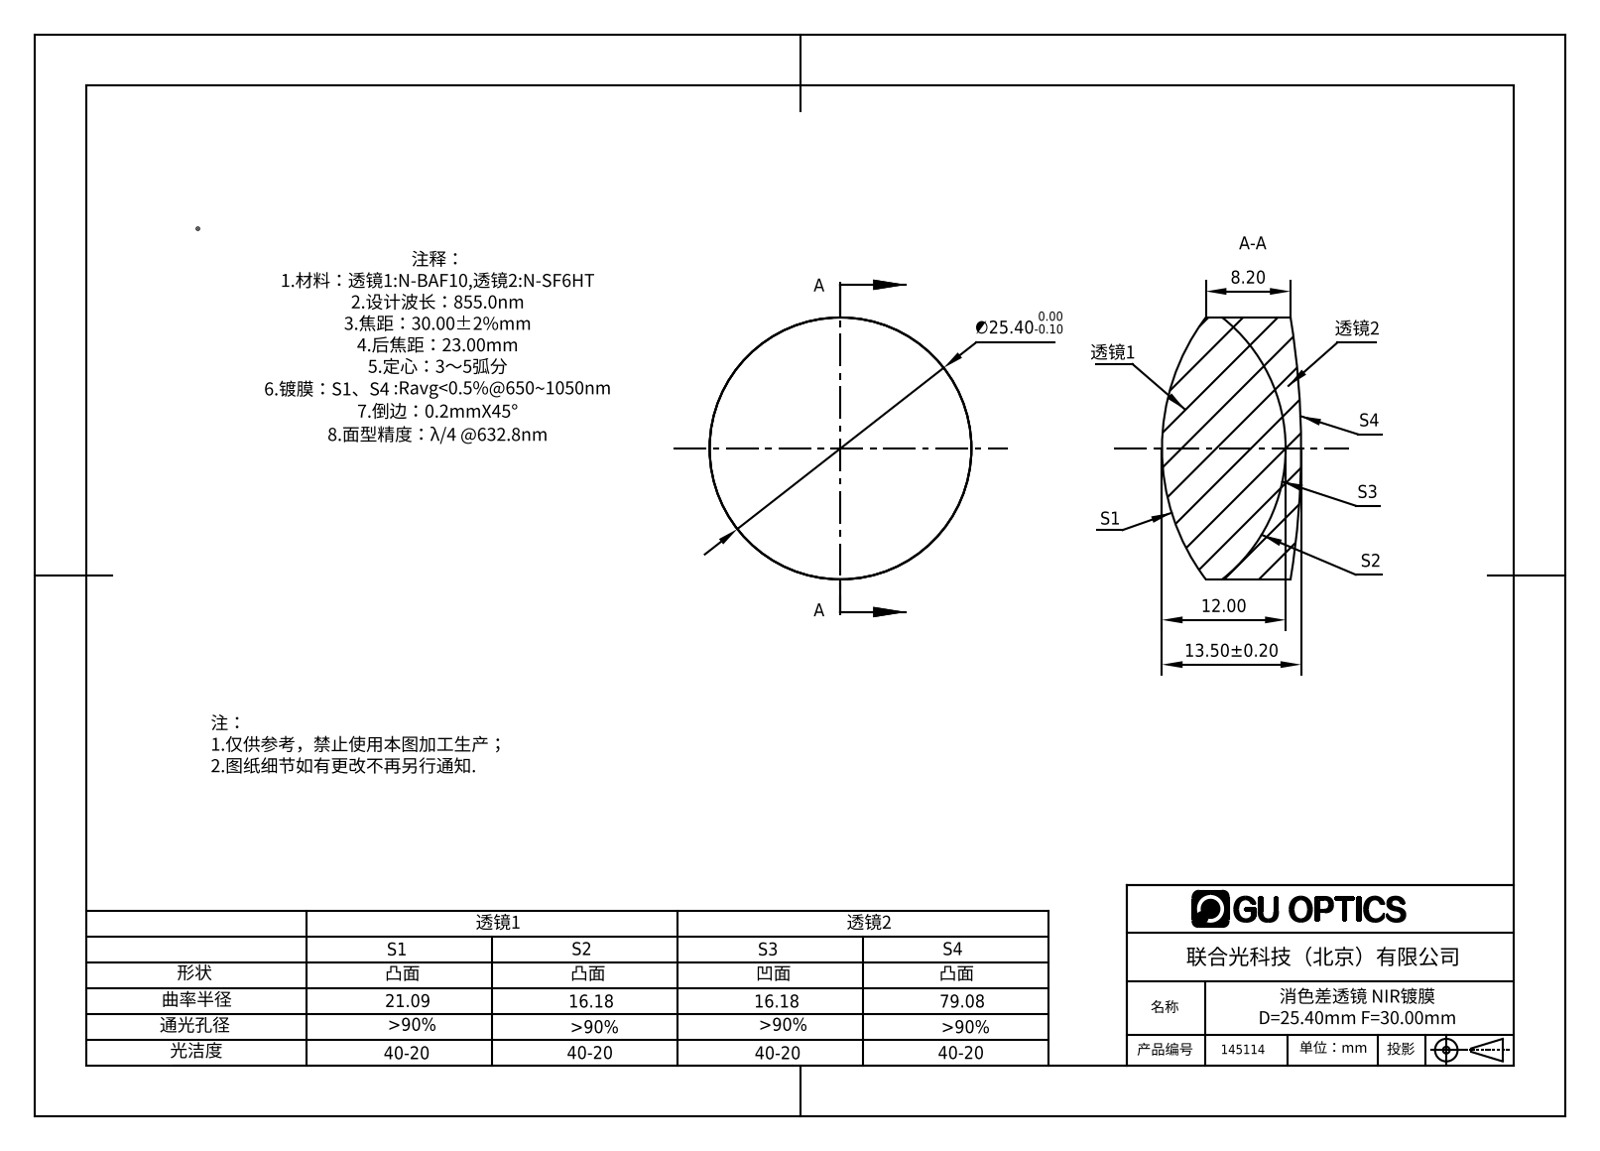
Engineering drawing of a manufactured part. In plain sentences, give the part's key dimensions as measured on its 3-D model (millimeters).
The part is named "145114". Its 3-D file was written by "SolidWorks 2016 (AUTOMOTIVE_DESIGN)". It is 2 solids with 12 faces: 0 planar, 4 cylindrical and 8 other. Overall it measures 25.4 by 25.4 by 13.5 millimeters. Its volume is 5 544 cubic millimeters and its surface area 2 981 square millimeters. Round bosses or shafts: 1 of diameter 25.4.
